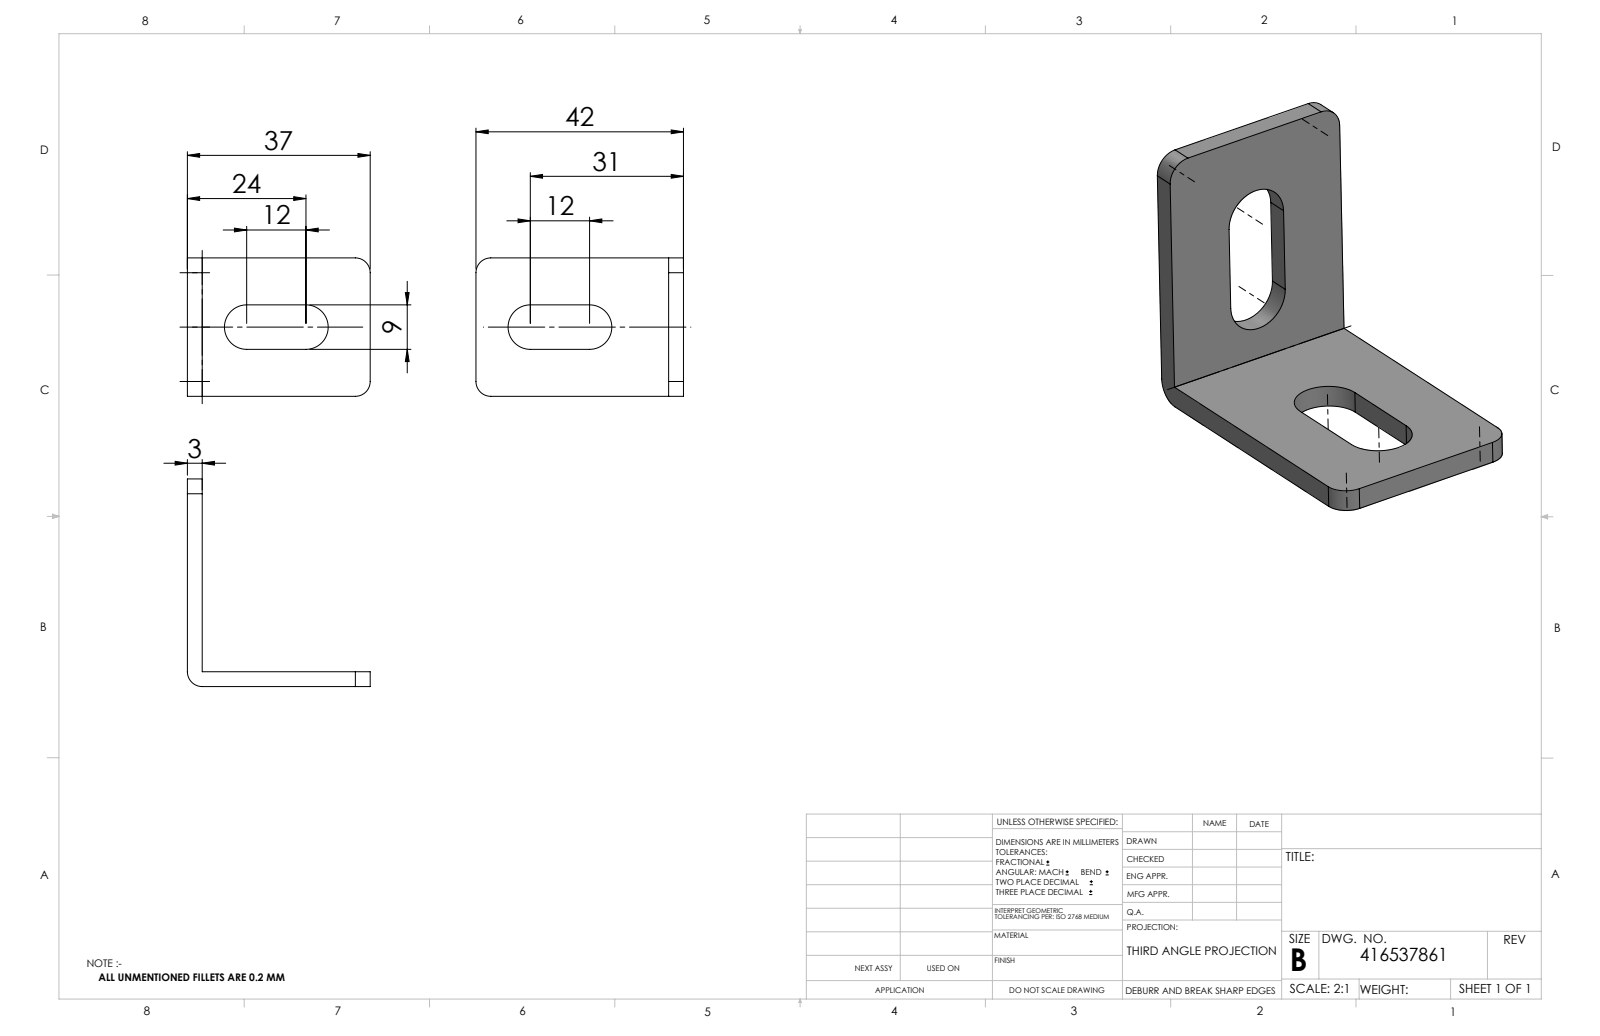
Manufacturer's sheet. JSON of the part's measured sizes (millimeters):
{"part_name": "537861; 416537861_c_1", "step_written_by": "SolidWorks 2014 (CONFIG_CONTROL_DESIGN)", "units": "millimeters", "bodies": {"solids": 1, "faces": 22, "planar": 12, "cylindrical": 10, "other": 0}, "overall_size": [42, 37, 28], "volume_mm3": 5277, "surface_area_mm2": 4436, "partial_cylinders_radius": [[3, 5], [4.5, 4]], "face_to_face_distances": [3, 28, 9.5, 18.5, 9, 37, 34, 42, 39]}
